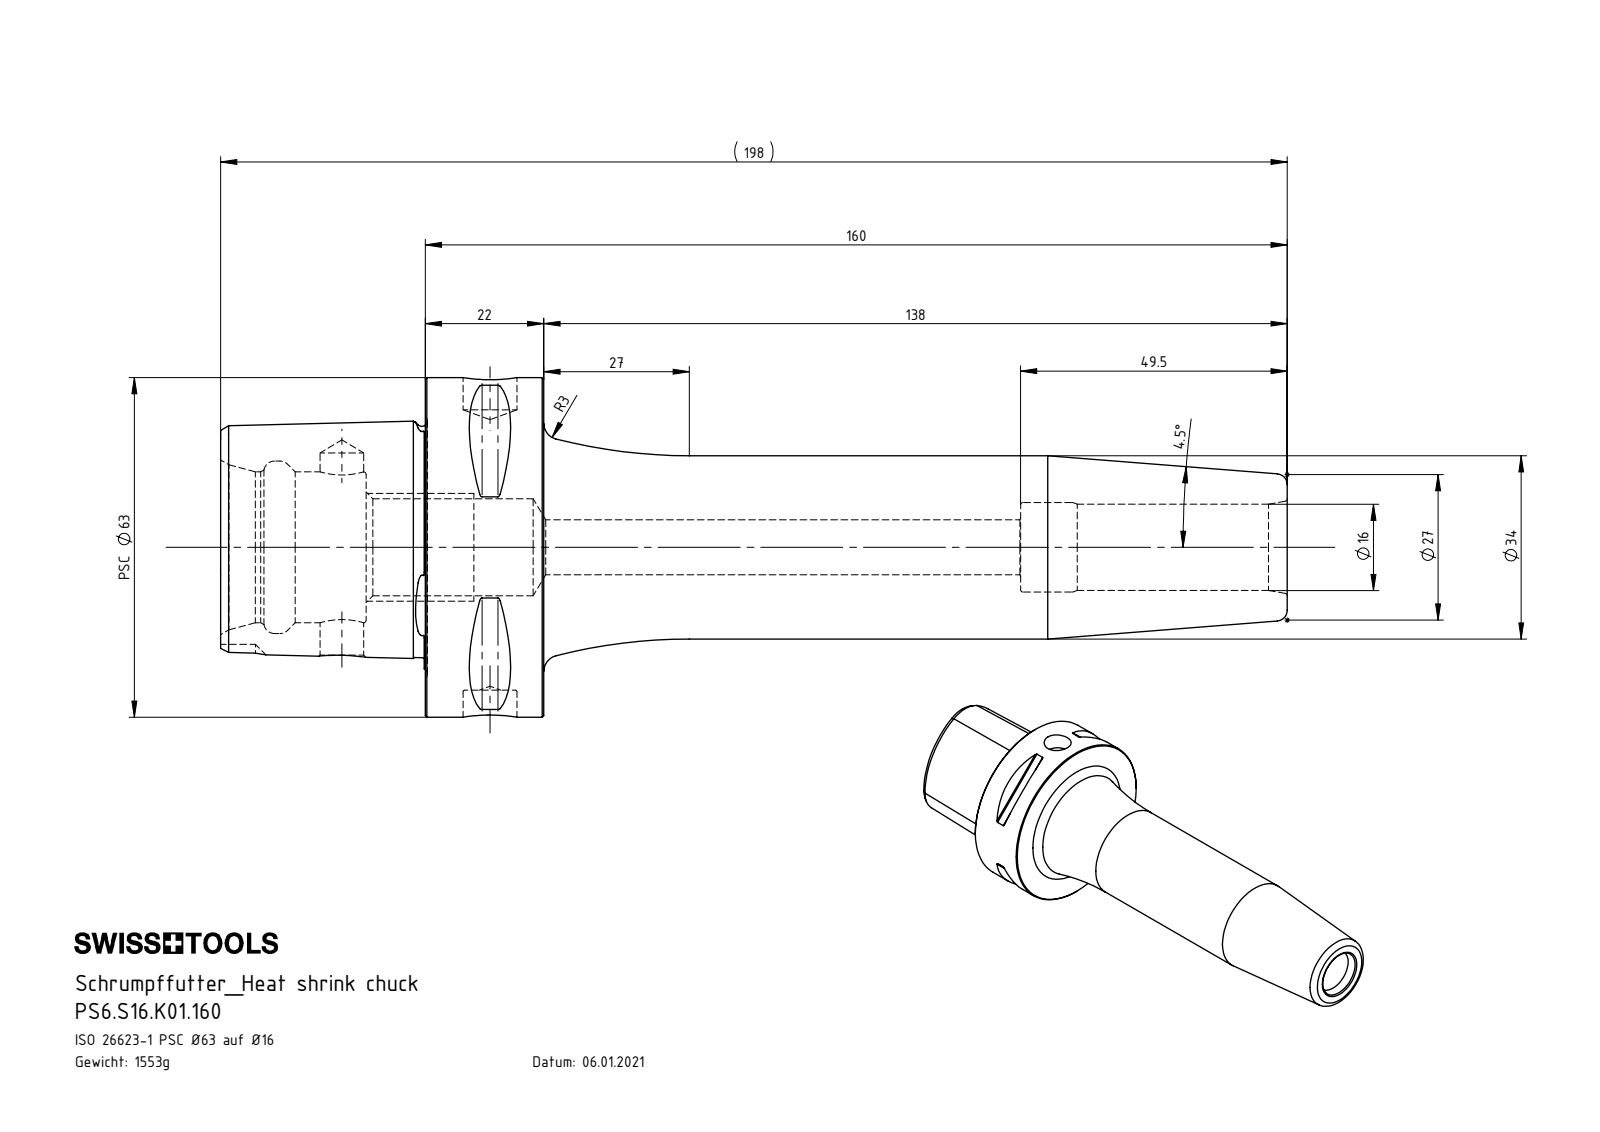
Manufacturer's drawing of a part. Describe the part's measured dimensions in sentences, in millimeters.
The part is named "PS6.S16.K01.160". Its 3-D file was written by "SolidWorks 2022 (AUTOMOTIVE_DESIGN)". It is 1 solid with 154 faces: 22 planar, 35 cylindrical and 97 other. Overall it measures 198 by 63 by 63 millimeters. Its volume is 197 796 cubic millimeters and its surface area 39 252 square millimeters. Round holes: 1 of diameter 8.1, 1 of diameter 10, 1 of diameter 10.2, 1 of diameter 16, 1 of diameter 16.6, 1 of diameter 18, 1 of diameter 28, 1 of diameter 32. Round bosses or shafts: 1 of diameter 63, 1 of diameter 34. Partial cylindrical surfaces (rounded edges, fillets, slot ends): 8 of radius 0.5, 1 of radius 6. The main face-to-face distances are 22, 38, 60, 24.88, 27, 11, 33, 55.8, 198, 171. The hole center spacings are 27.5.
